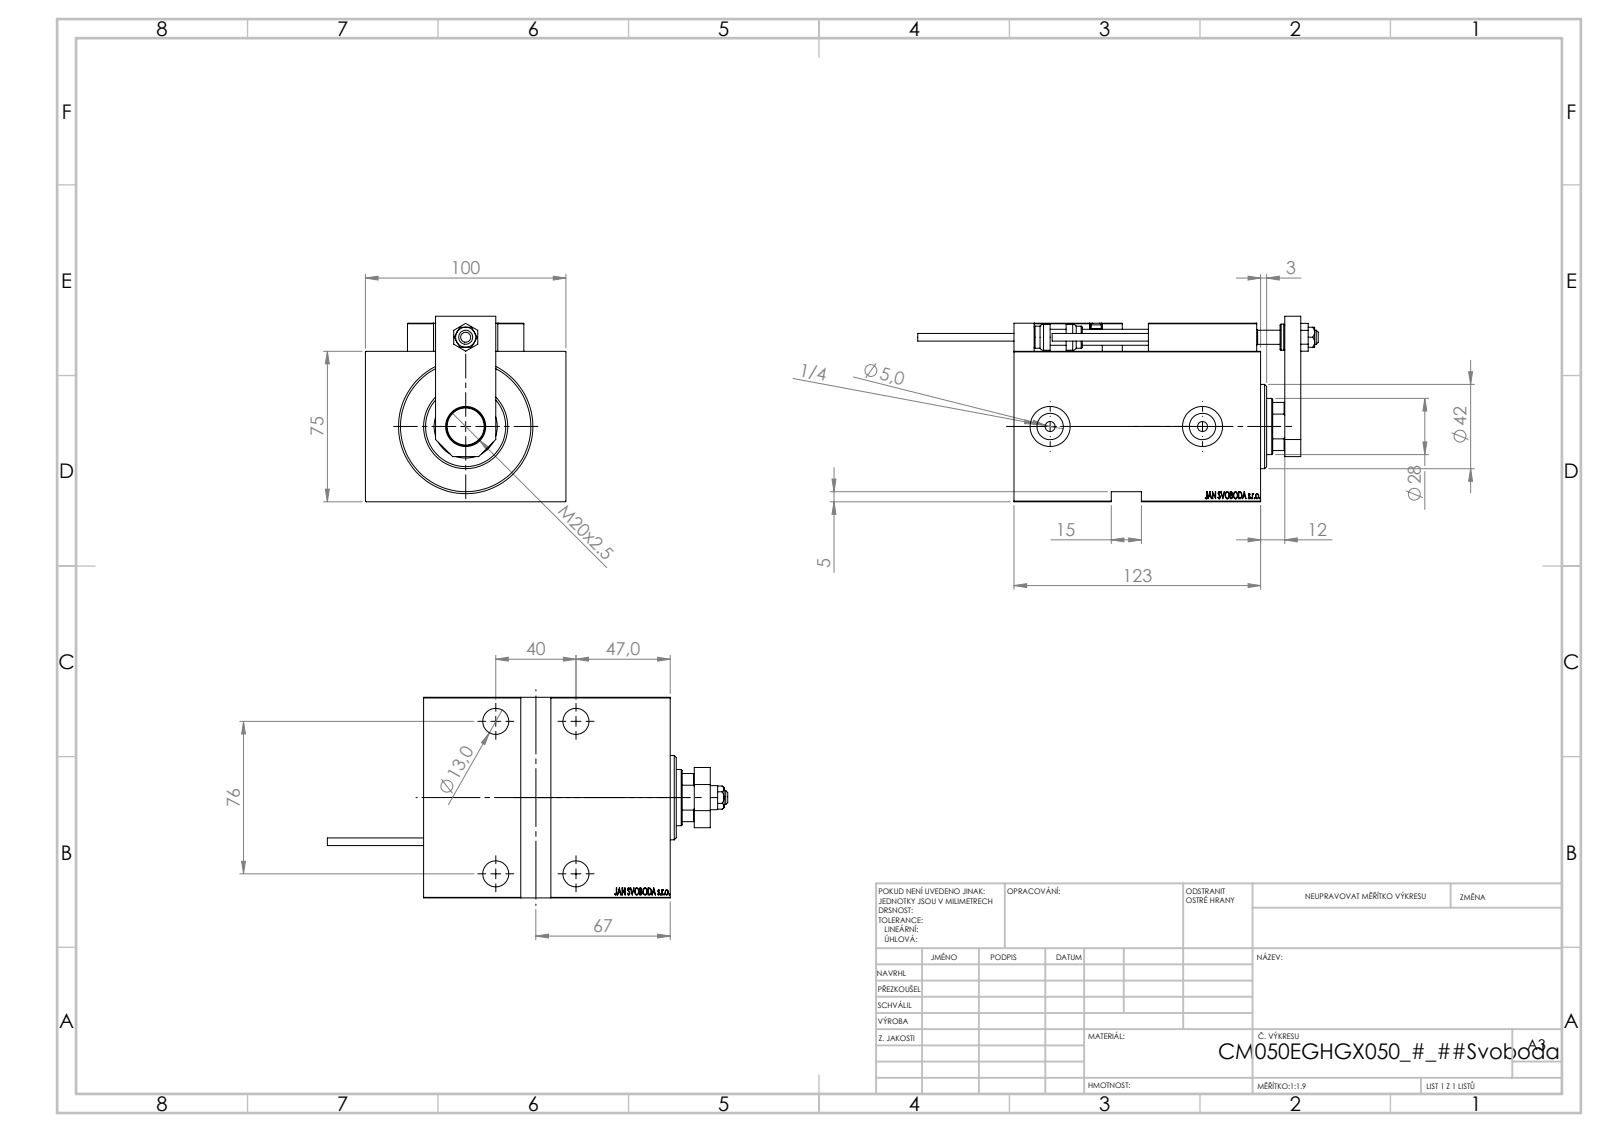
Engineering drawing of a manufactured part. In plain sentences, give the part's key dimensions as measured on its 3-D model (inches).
The part is named "NUT_D12; SWITCH X; V450CM_VC_B; SWITCH DIM B,W (+8 more)". Its 3-D file was written by "SolidWorks 2019 (CONFIG_CONTROL_DESIGN)". It is 24 solids with 1293 faces: 570 planar, 182 cylindrical and 541 other. Overall it measures 7.862 by 3.937 by 3.642 inches. Its volume is 52.29 cubic inches and its surface area 228.9 square inches. Round holes: 5 of diameter 0.315, 4 of diameter 0.126, 4 of diameter 0.157, 4 of diameter 0.197, 4 of diameter 0.512, 4 of diameter 0.748, 3 of diameter 0.787, 2 of diameter 0.518, 1 of diameter 0.276, 1 of diameter 0.728, 1 of diameter 1.102, 1 of diameter 1.24. Round bosses or shafts: 2 of diameter 0.197, 2 of diameter 0.15, 1 of diameter 2.047, 1 of diameter 1.654, 1 of diameter 0.512, 1 of diameter 0.433. Partial cylindrical surfaces (rounded edges, fillets, slot ends): 30 of radius 0.012, 2 of radius 0.118, 1 of radius 0.531. The main face-to-face distances are 2.953, 3.937, 0.551, 4.843, 0.197, 4.291, 0.472, 0.787, 0.984, 0.669. The hole center spacings are 2.992, 0.448, 0.787, 1.165, 1.169, 1.42, 1.575, 1.644.
